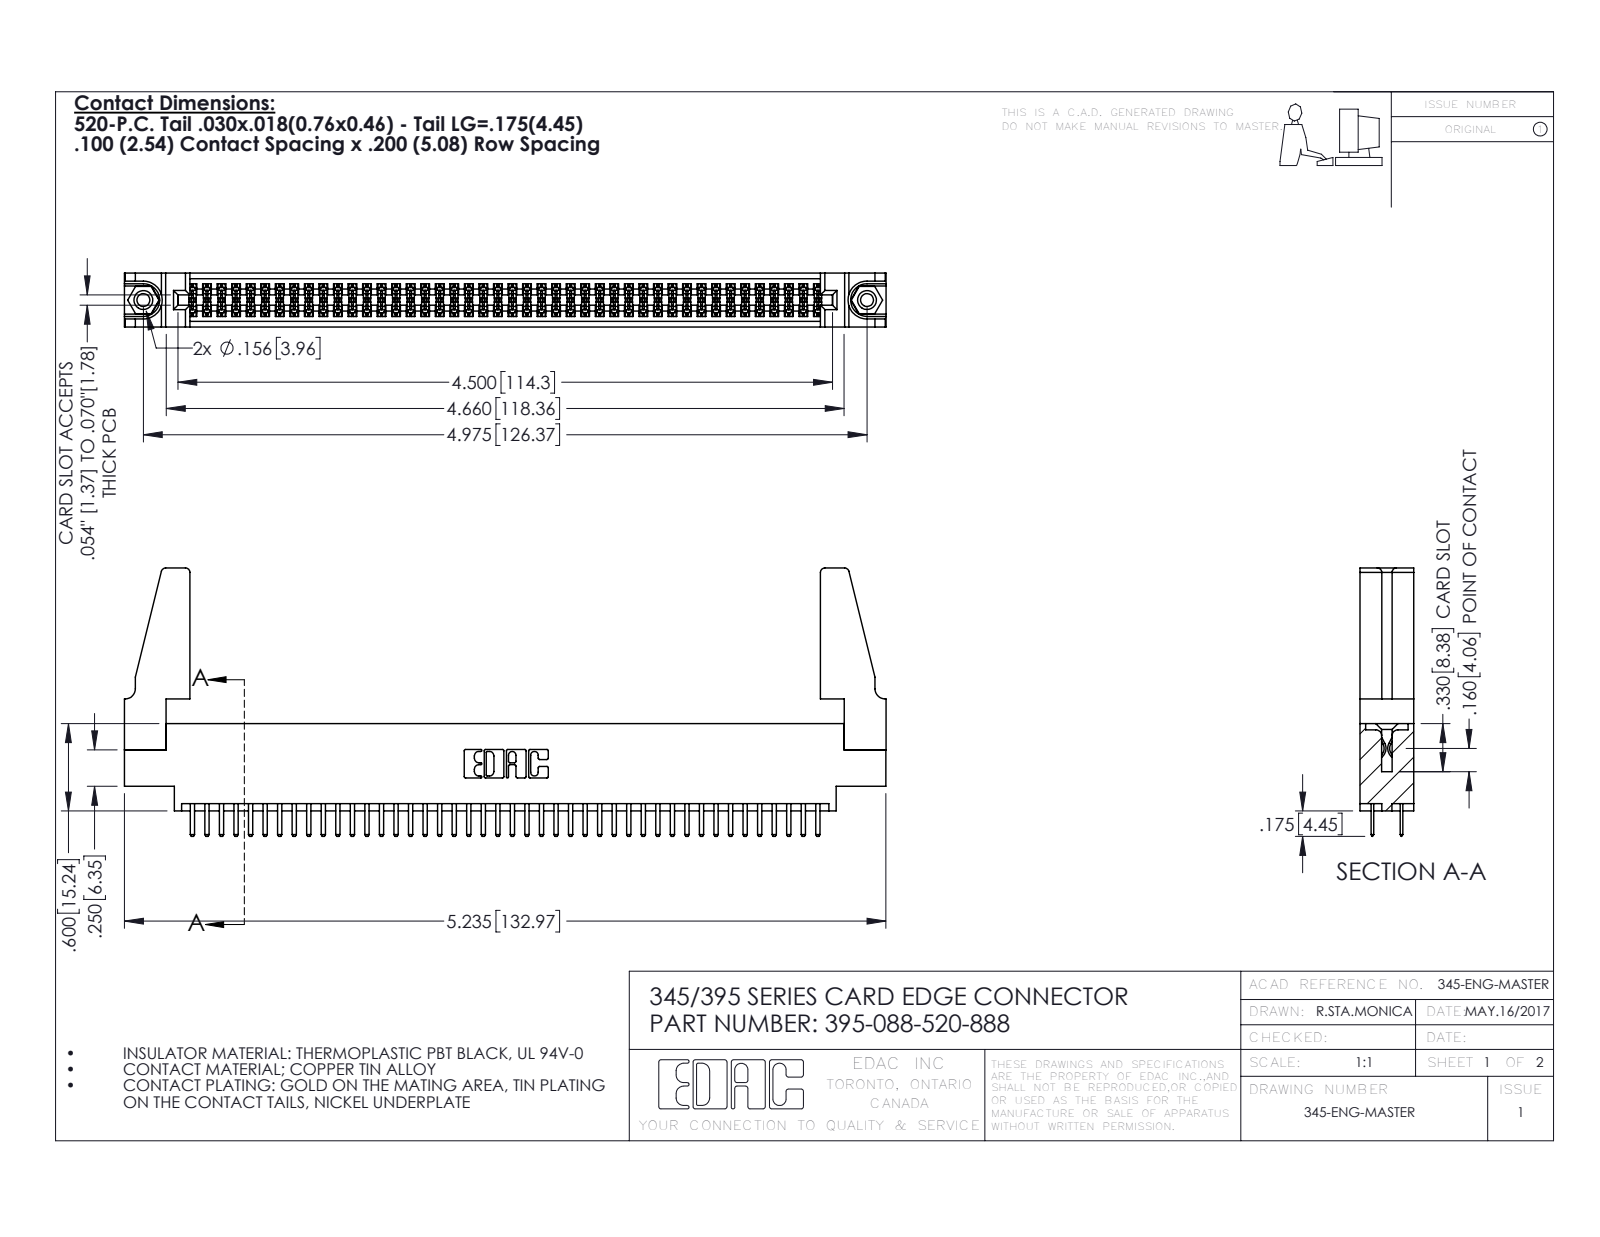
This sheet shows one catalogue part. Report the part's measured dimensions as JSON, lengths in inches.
{"part_name": "345 Part_0.170 Offset - 0.156 Dia-TH; 345-292-001_345-293-120; 395-088-520-888; 345-250-001_345-250-001-102 (+1 more)", "step_written_by": "SolidWorks 2016 (CONFIG_CONTROL_DESIGN)", "units": "inches", "bodies": {"solids": 93, "faces": 5006, "planar": 3236, "cylindrical": 1754, "other": 16}, "overall_size": [5.236, 1.845, 0.37], "volume_in3": 0.979, "surface_area_in2": 34.29, "round_holes": [[0.089, 2], [0.125, 2], [0.156, 2], [0.064, 1]], "round_bosses_or_shafts": [[0.155, 2]], "partial_cylinders_radius": [[0.006, 132], [0.01, 92], [0.01, 22], [0.03, 8], [0.007, 6], [0.031, 6], [0.026, 3], [0.014, 2]], "face_to_face_distances": [0.072, 0.298, 0.37, 0.2, 0.098, 0.272, 0.025, 0.225, 0.022, 0.175], "hole_center_spacings": [0.27, 4.739, 4.975]}
